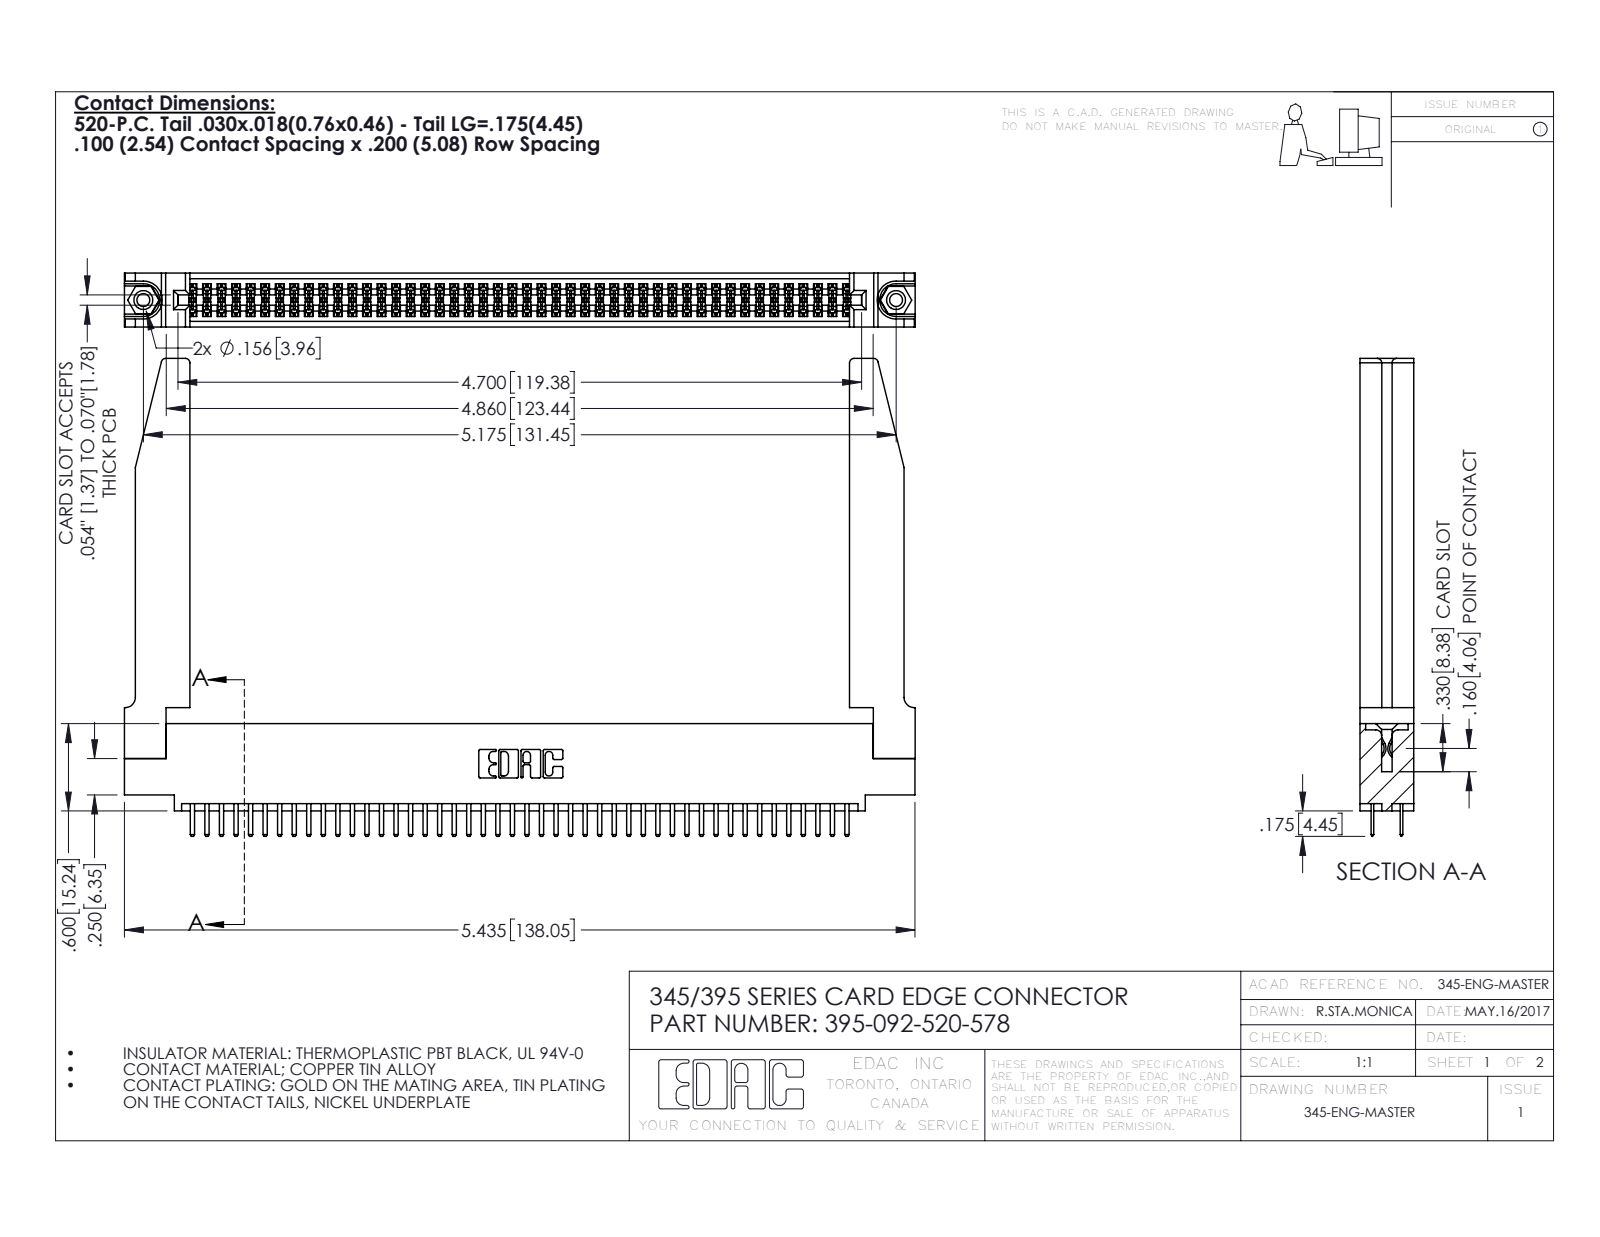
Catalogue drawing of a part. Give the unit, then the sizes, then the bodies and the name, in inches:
Units: inches
Overall size (bounding box): 5.436 × 3.285 × 0.37
Round holes (diameter × count): ⌀0.089 ×2, ⌀0.125 ×2, ⌀0.156 ×2, ⌀0.064 ×1
Round bosses / shafts (diameter × count): ⌀0.155 ×2
Partial cylindrical surfaces — rounded edges, fillets, slot ends (radius × count): R0.006 ×138, R0.01 ×96, R0.01 ×22, R0.03 ×8, R0.007 ×6, R0.031 ×6, R0.026 ×3, R0.014 ×2
Main face-to-face distances: 0.37, 0.072, 0.298, 0.2, 0.098, 0.272, 0.025, 0.225, 0.022, 0.072
Hole centre spacings: 0.27, 4.939, 5.175
Volume: 1.288 in³ · Surface area: 41.29 in²
Bodies: 97 solids, 5332 faces (3446 planar, 1834 cylindrical, 52 other)
Part name (STEP PRODUCT): 345 Part_0.110 Offset - 0.156 Dia-TH; 395-092-520-578; 345-220-078_345-220-078; 345-292-001_345-293-120 (+1 more)
STEP written by: SolidWorks 2016 (CONFIG_CONTROL_DESIGN)
